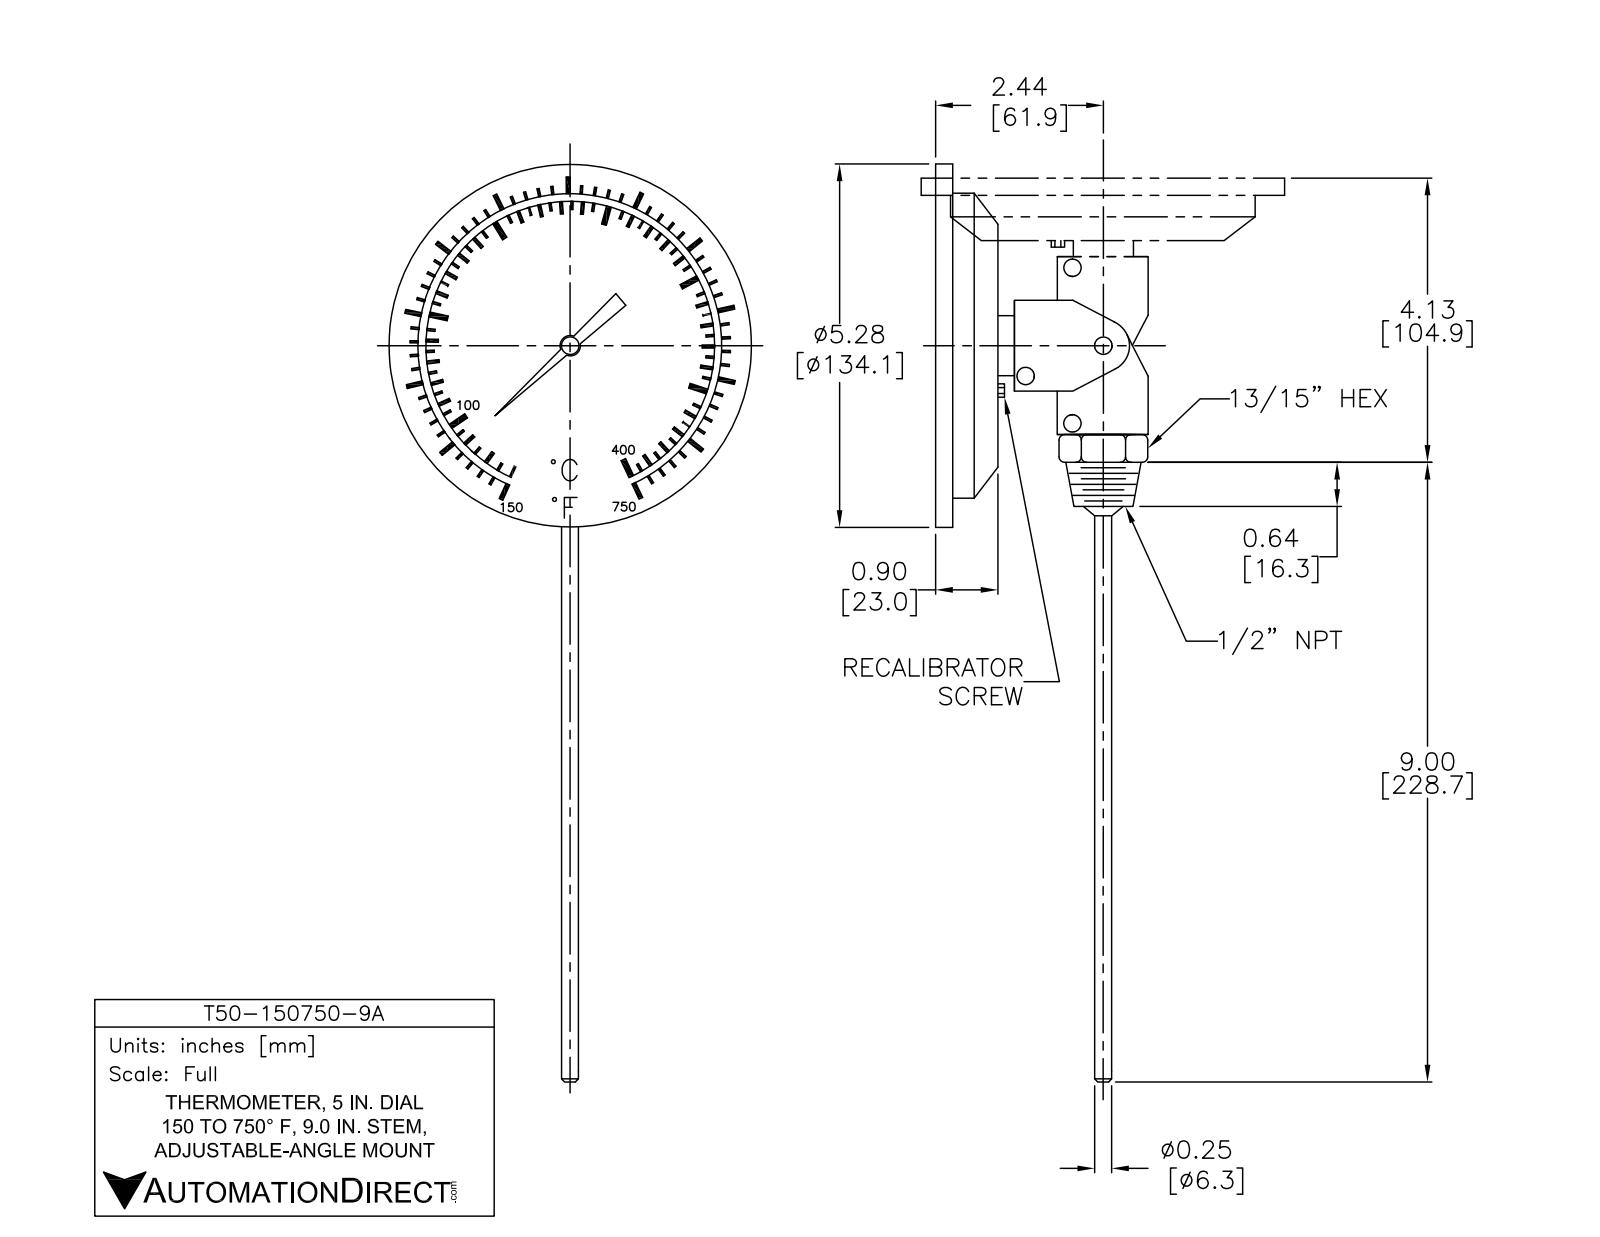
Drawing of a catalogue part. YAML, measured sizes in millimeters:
part_name: "T50-150750-9A"
step_written_by: "SolidWorks 2021 (AUTOMOTIVE_DESIGN)"
units: millimeters
bodies: {solids: 1, faces: 499, planar: 296, cylindrical: 45, other: 158}
overall_size: [326.6, 134.1, 134.1]
volume: 169900
surface_area: 64900
round_holes:
  - {diameter: 87, count: 1}
  - {diameter: 94.1, count: 1}
  - {diameter: 120.9, count: 1}
  - {diameter: 122.8, count: 1}
round_bosses_or_shafts:
  - {diameter: 7.7, count: 4}
  - {diameter: 3.7, count: 2}
  - {diameter: 134.1, count: 1}
  - {diameter: 126.2, count: 1}
  - {diameter: 87.7, count: 1}
  - {diameter: 21.6, count: 1}
  - {diameter: 20.9, count: 1}
  - {diameter: 13.8, count: 1}
partial_cylinders:
  - {radius: 1.5, count: 10}
  - {radius: 1, count: 4}
  - {radius: 4.3, count: 1}
  - {radius: 8.5, count: 1}
  - {radius: 8.5, count: 1}
  - {radius: 8.7, count: 1}
  - {radius: 10.2, count: 1}
  - {radius: 47.4, count: 1}
face_to_face_distances: [9, 1.9, 1.4, 10.8, 30.2, 20.7, 11.7, 9.9, 31.6, 61.8]
